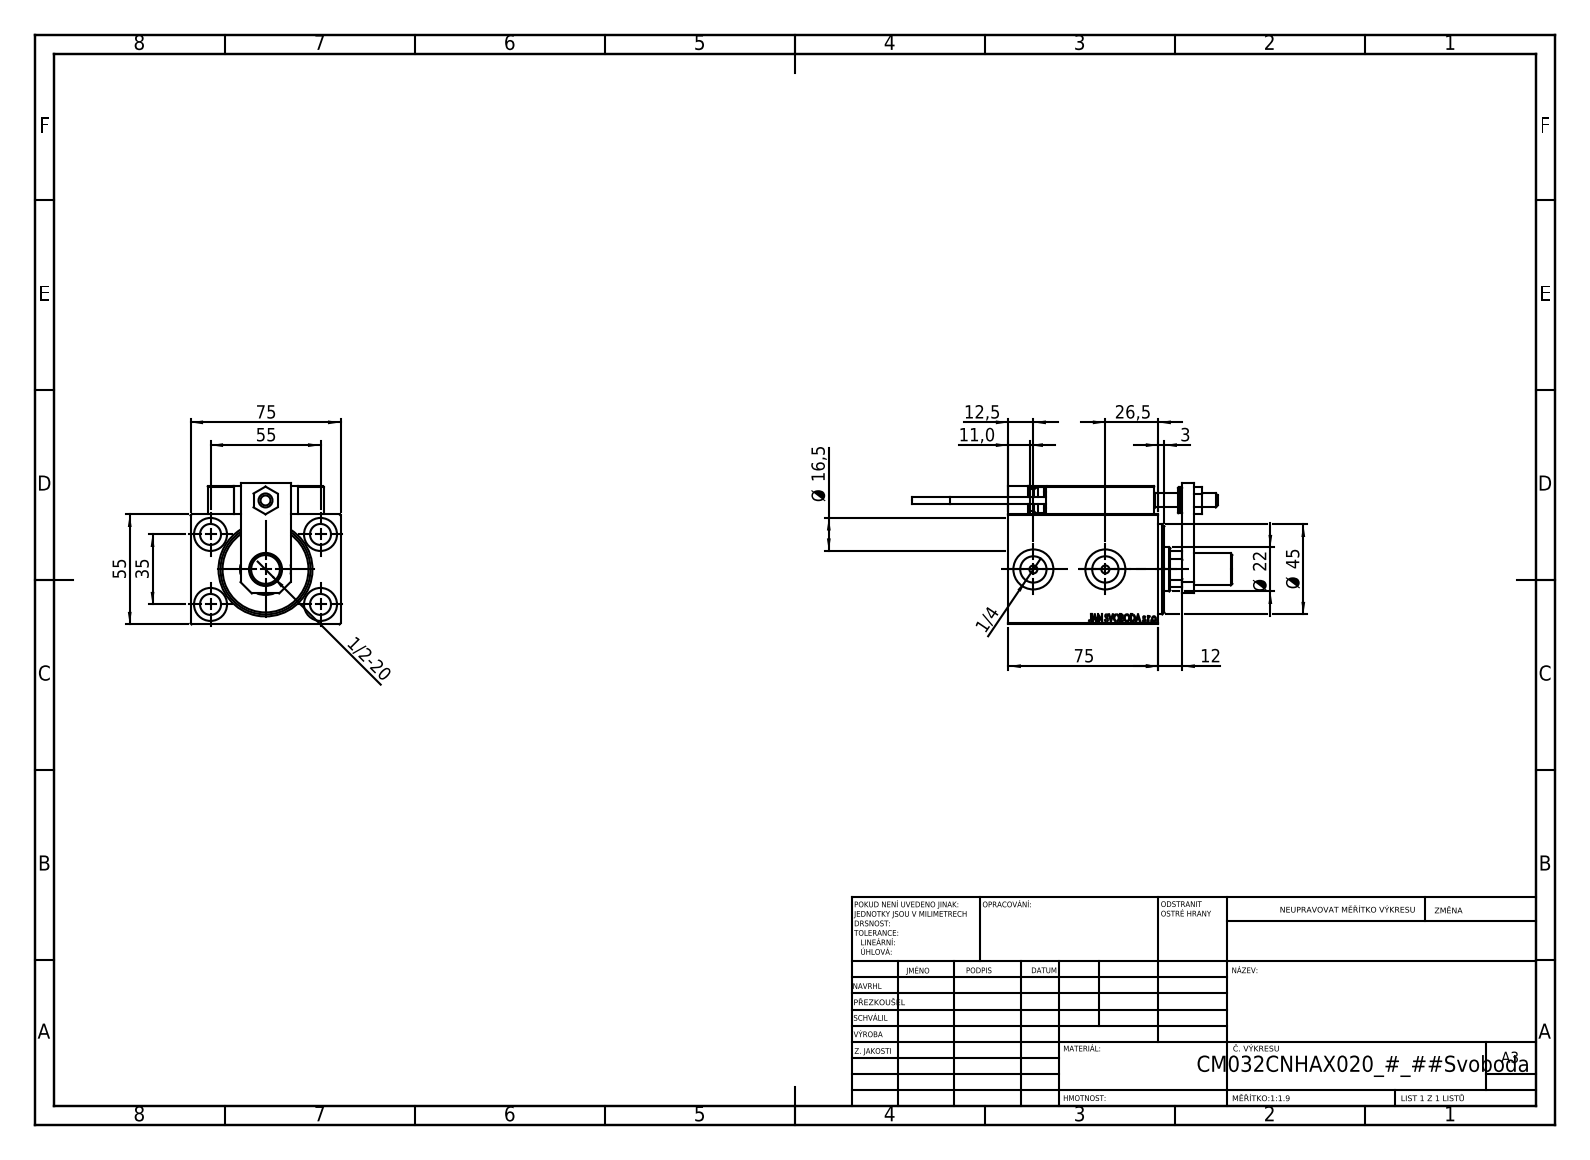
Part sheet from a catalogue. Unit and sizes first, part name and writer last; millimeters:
Units: millimetres
Overall size (bounding box): 160 × 75 × 70.5
Round holes (diameter × count): ⌀4 ×6, ⌀8 ×5, ⌀10.5 ×5, ⌀16.5 ×5, ⌀3.2 ×4, ⌀5 ×2, ⌀13.16 ×2, ⌀20 ×2, ⌀7 ×1, ⌀22 ×1, ⌀25.5 ×1, ⌀32 ×1
Round bosses / shafts (diameter × count): ⌀5 ×2, ⌀3.8 ×2, ⌀16 ×1, ⌀14 ×1, ⌀13 ×1, ⌀11 ×1
Partial cylindrical surfaces — rounded edges, fillets, slot ends (radius × count): R0.3 ×30, R3 ×2, R10.5 ×1
Main face-to-face distances: 55, 75, 14, 10, 12, 69, 7, 25, 20, 15
Hole centre spacings: 32.6, 11.37, 20, 27.07, 29.59, 29.69, 32.33, 34.83
Volume: 318 110 mm³ · Surface area: 86 141 mm²
Bodies: 24 solids, 1295 faces (563 planar, 192 cylindrical, 540 other)
Part name (STEP PRODUCT): ALLEN BOLT D5; MAGNET; SWITCH X; ALLEN BOLT D8 (+7 more)
STEP written by: SolidWorks 2019 (CONFIG_CONTROL_DESIGN)
